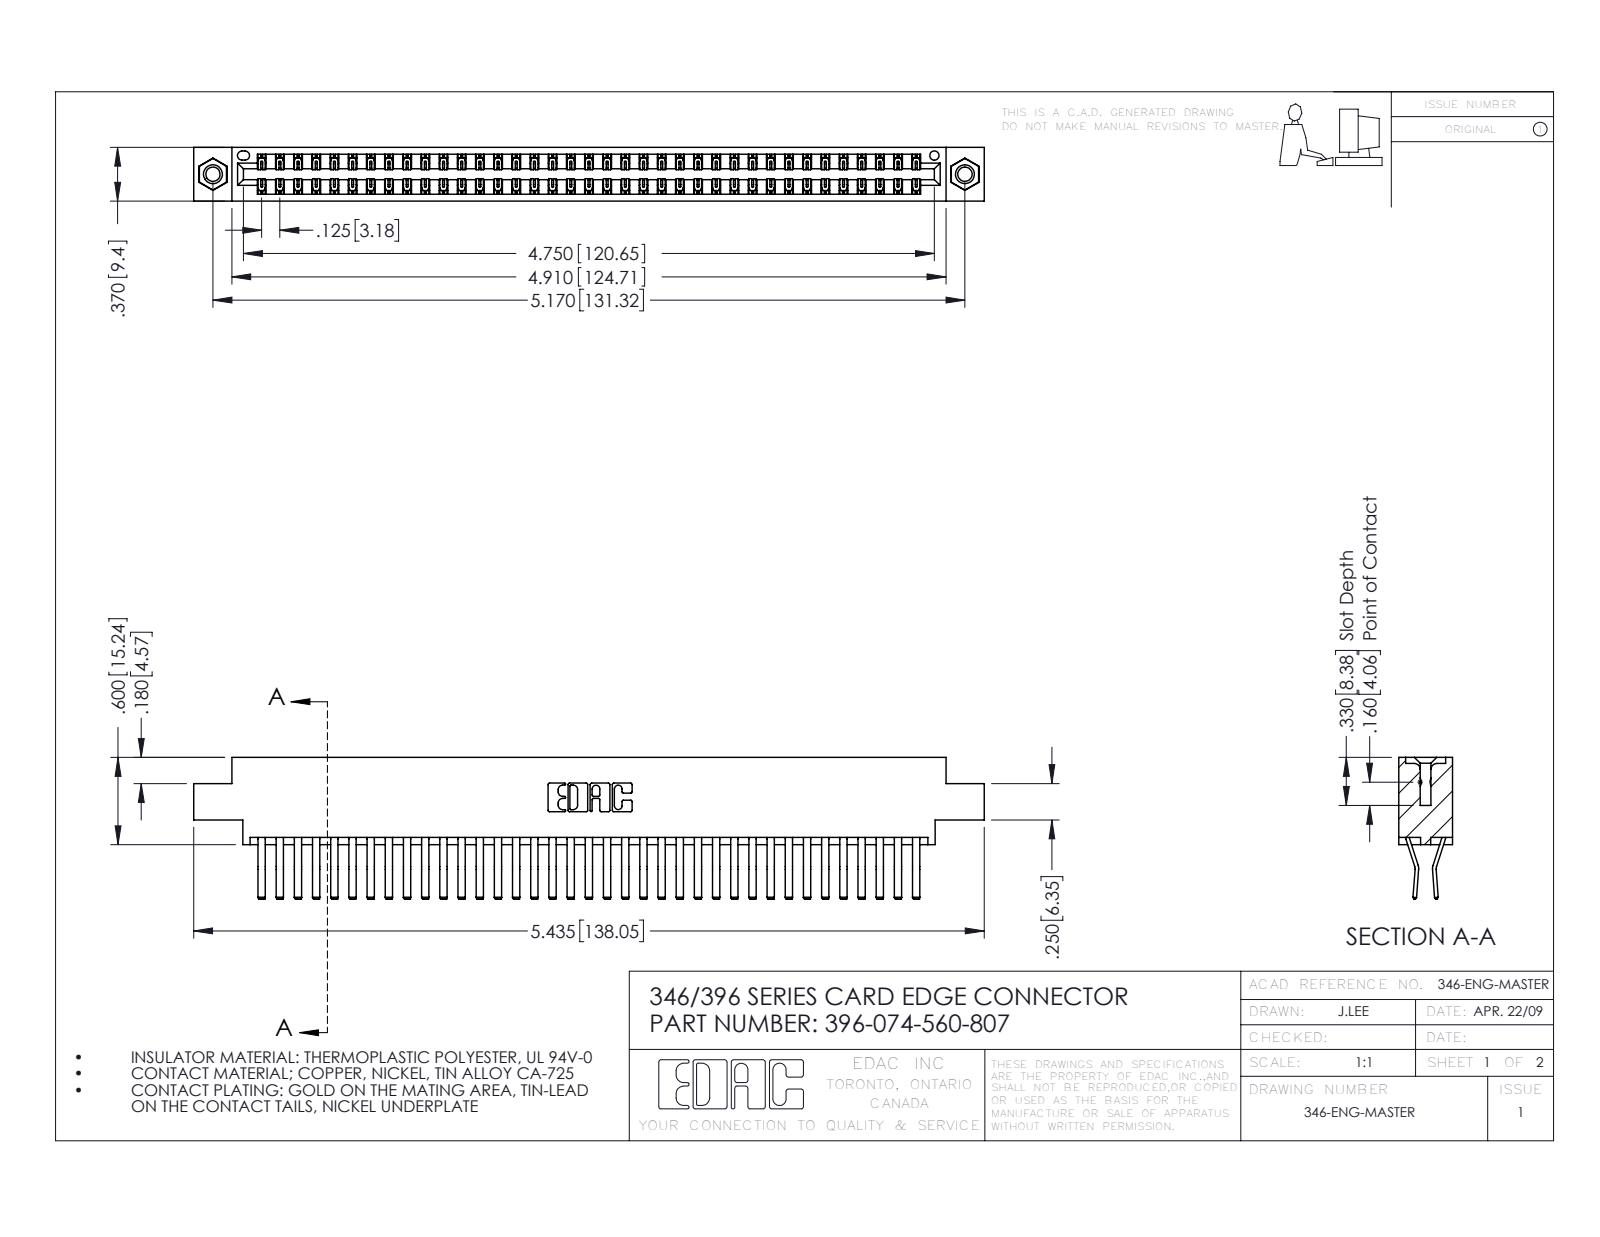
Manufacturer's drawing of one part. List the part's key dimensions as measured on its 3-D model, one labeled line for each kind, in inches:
Part name (STEP PRODUCT): 346 Part_0.170 Offset - 0.156 Dia-TI; 345-250-001_345-250-005-103; 396-074-560-807; 345-292-001_560 Tail
STEP written by: SolidWorks 2016 (CONFIG_CONTROL_DESIGN)
Units: inches
Bodies: 77 solids, 4182 faces (2702 planar, 1464 cylindrical, 16 other)
Overall size (bounding box): 5.435 × 0.975 × 0.37
Volume: 0.838 in³ · Surface area: 31.49 in²
Round holes (diameter × count): ⌀0.098 ×2, ⌀0.125 ×2, ⌀0.156 ×2, ⌀0.064 ×1
Round bosses / shafts (diameter × count): ⌀0.155 ×2
Partial cylindrical surfaces — rounded edges, fillets, slot ends (radius × count): R0.006 ×111, R0.01 ×22, R0.007 ×6, R0.031 ×6, R0.026 ×3, R0.01 ×2, R0.014 ×2, R0.022 ×2
Main face-to-face distances: 0.048, 0.322, 0.37, 0.025, 0.25, 0.072, 0.298, 0.275, 0.222, 0.148
Hole centre spacings: 0.246, 4.961, 5.17
